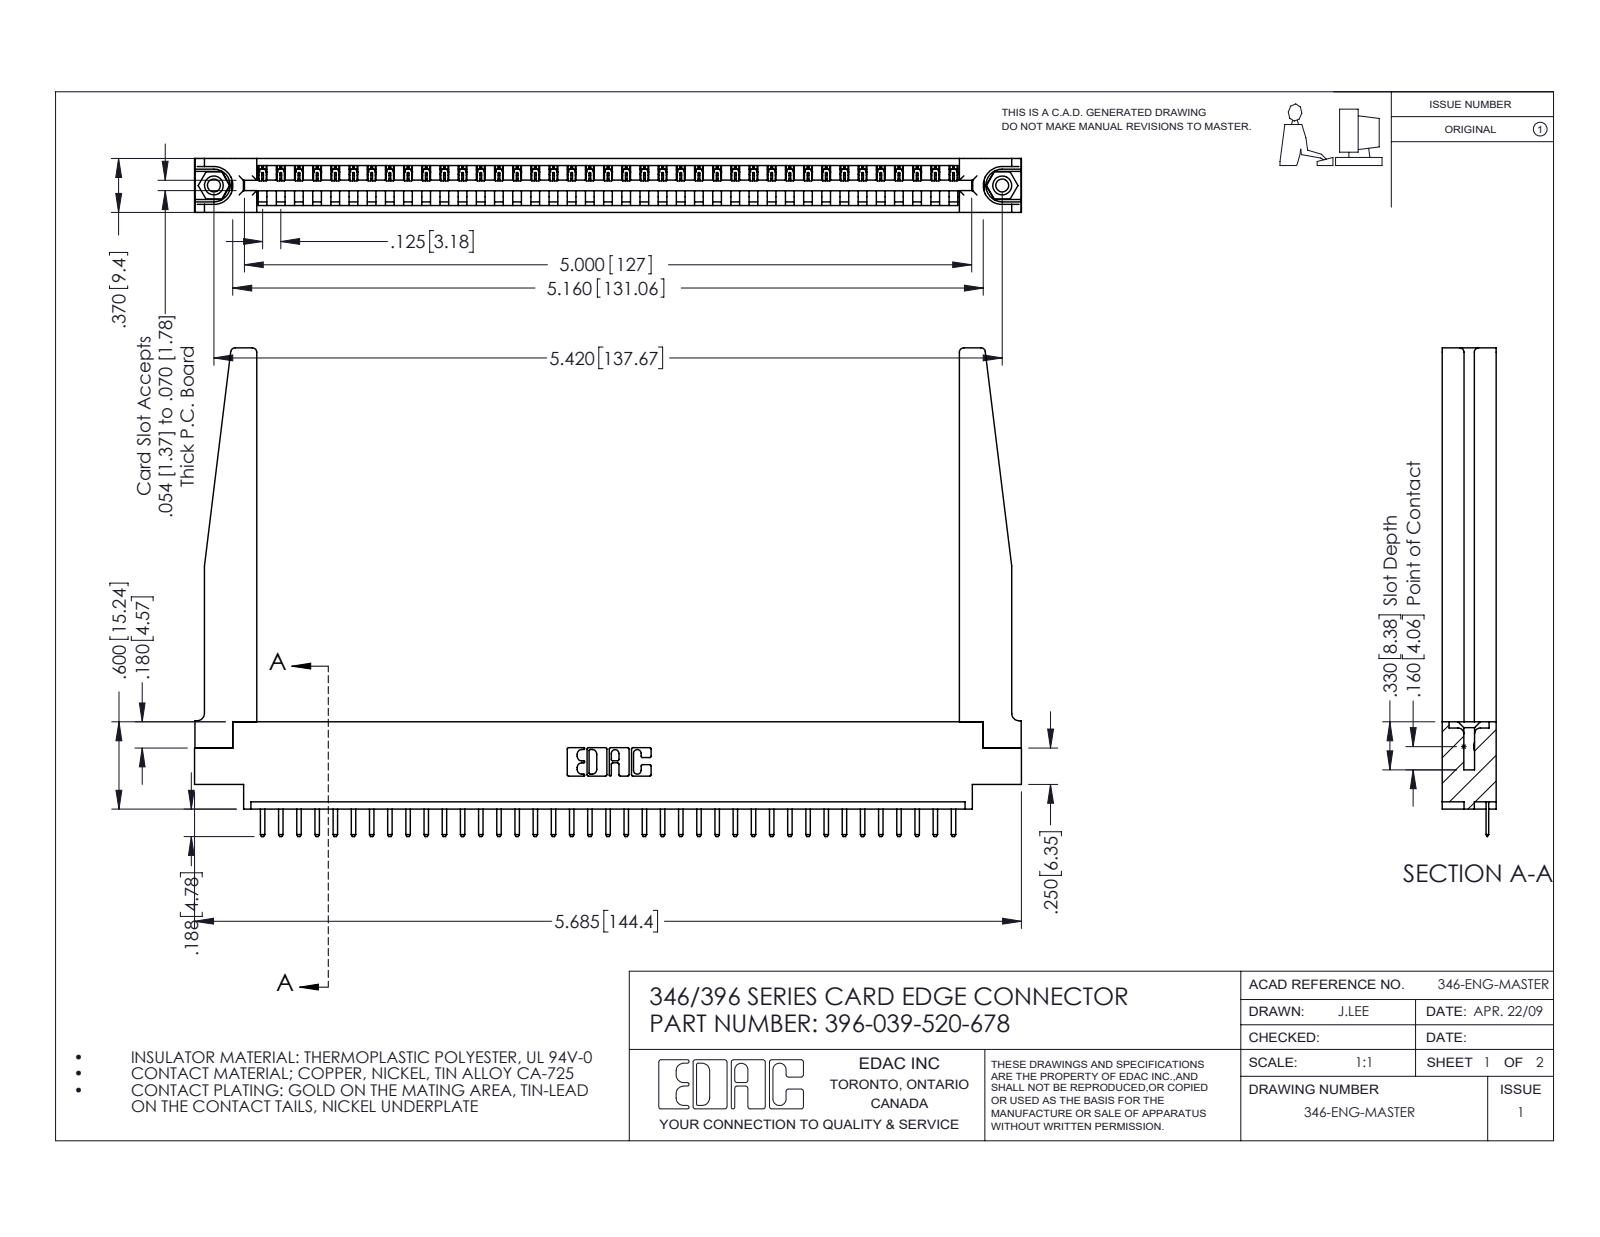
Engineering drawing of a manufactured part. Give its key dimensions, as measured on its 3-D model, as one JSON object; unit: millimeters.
{"part_name": "345-250-001_345-250-001-102; 346-220-078_345-220-078; 345-292-001_345-293-120; 346 Part_0.170 Offset - 0.156 Dia-TH (+1 more)", "step_written_by": "SolidWorks 2016 (CONFIG_CONTROL_DESIGN)", "units": "millimeters", "bodies": {"solids": 44, "faces": 2778, "planar": 1860, "cylindrical": 866, "other": 52}, "overall_size": [144.4, 85.3, 9.4], "volume_mm3": 20450, "surface_area_mm2": 23210, "round_holes": [[2.3, 2], [3.2, 2], [4, 2], [1.6, 1]], "round_bosses_or_shafts": [[3.9, 2]], "partial_cylinders_radius": [[0.3, 80], [0.2, 78], [0.3, 22], [0.8, 8], [0.2, 6], [0.8, 6], [0.7, 3], [0.8, 2]], "face_to_face_distances": [9.4, 1.2, 8.2, 3.8, 1.8, 3.8, 6.4, 5.6, 2.5, 4.4], "hole_center_spacings": [6.2, 132.4, 137.7]}
